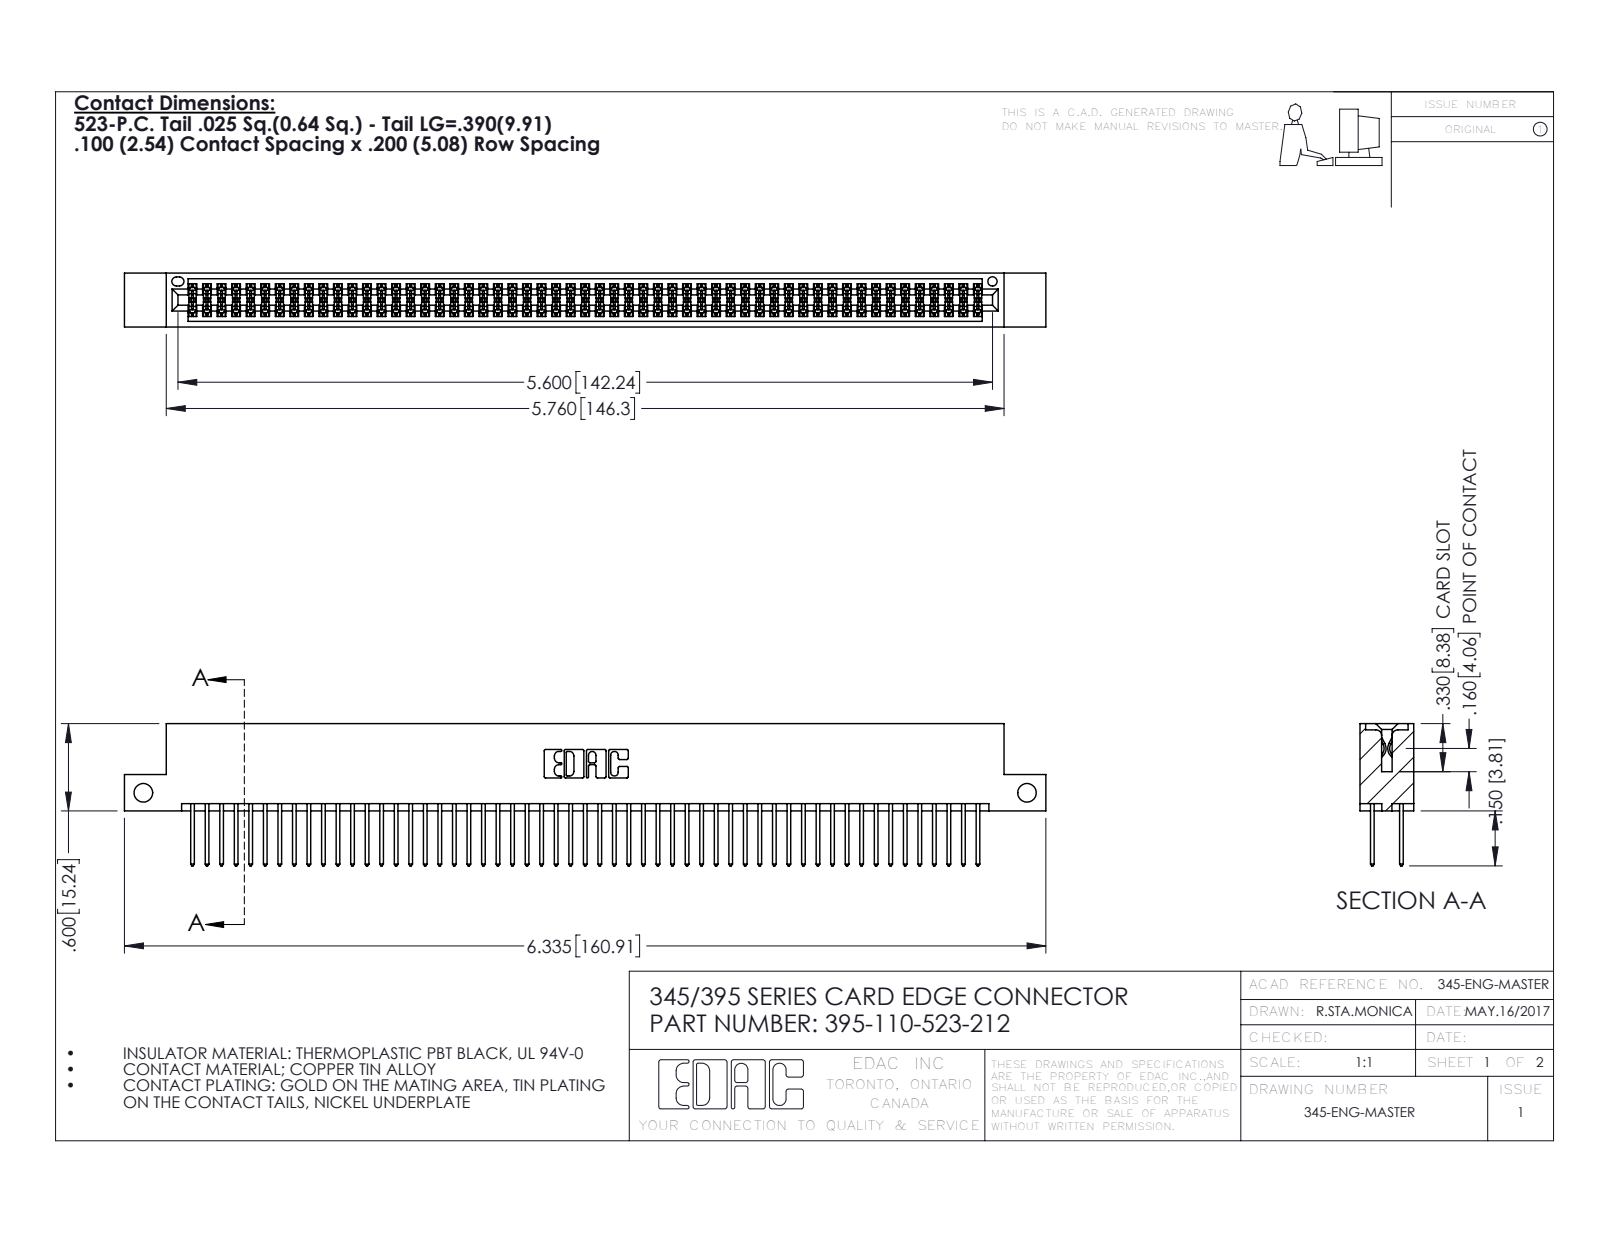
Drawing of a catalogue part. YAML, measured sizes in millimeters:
part_name: "395-110-523-212; 345-292-001_345-293-123; 345 Part_Flush Mounting Lugs - Side Mount"
step_written_by: "SolidWorks 2016 (CONFIG_CONTROL_DESIGN)"
units: millimeters
bodies: {solids: 111, faces: 5626, planar: 3710, cylindrical: 1916, other: 0}
overall_size: [160.9, 24.8, 9.4]
volume: 15900
surface_area: 24610
round_holes:
  - {diameter: 3.3, count: 2}
  - {diameter: 1.6, count: 1}
partial_cylinders:
  - {radius: 0.2, count: 165}
  - {radius: 0.3, count: 110}
  - {radius: 0.3, count: 22}
  - {radius: 0.2, count: 6}
  - {radius: 0.8, count: 6}
  - {radius: 0.7, count: 3}
  - {radius: 0.4, count: 2}
  - {radius: 0.5, count: 2}
face_to_face_distances: [7.6, 1.8, 5.1, 2.5, 6.9, 0.6, 9.4, 5.7, 4.4, 3.8]
hole_center_spacings: [154.3]
